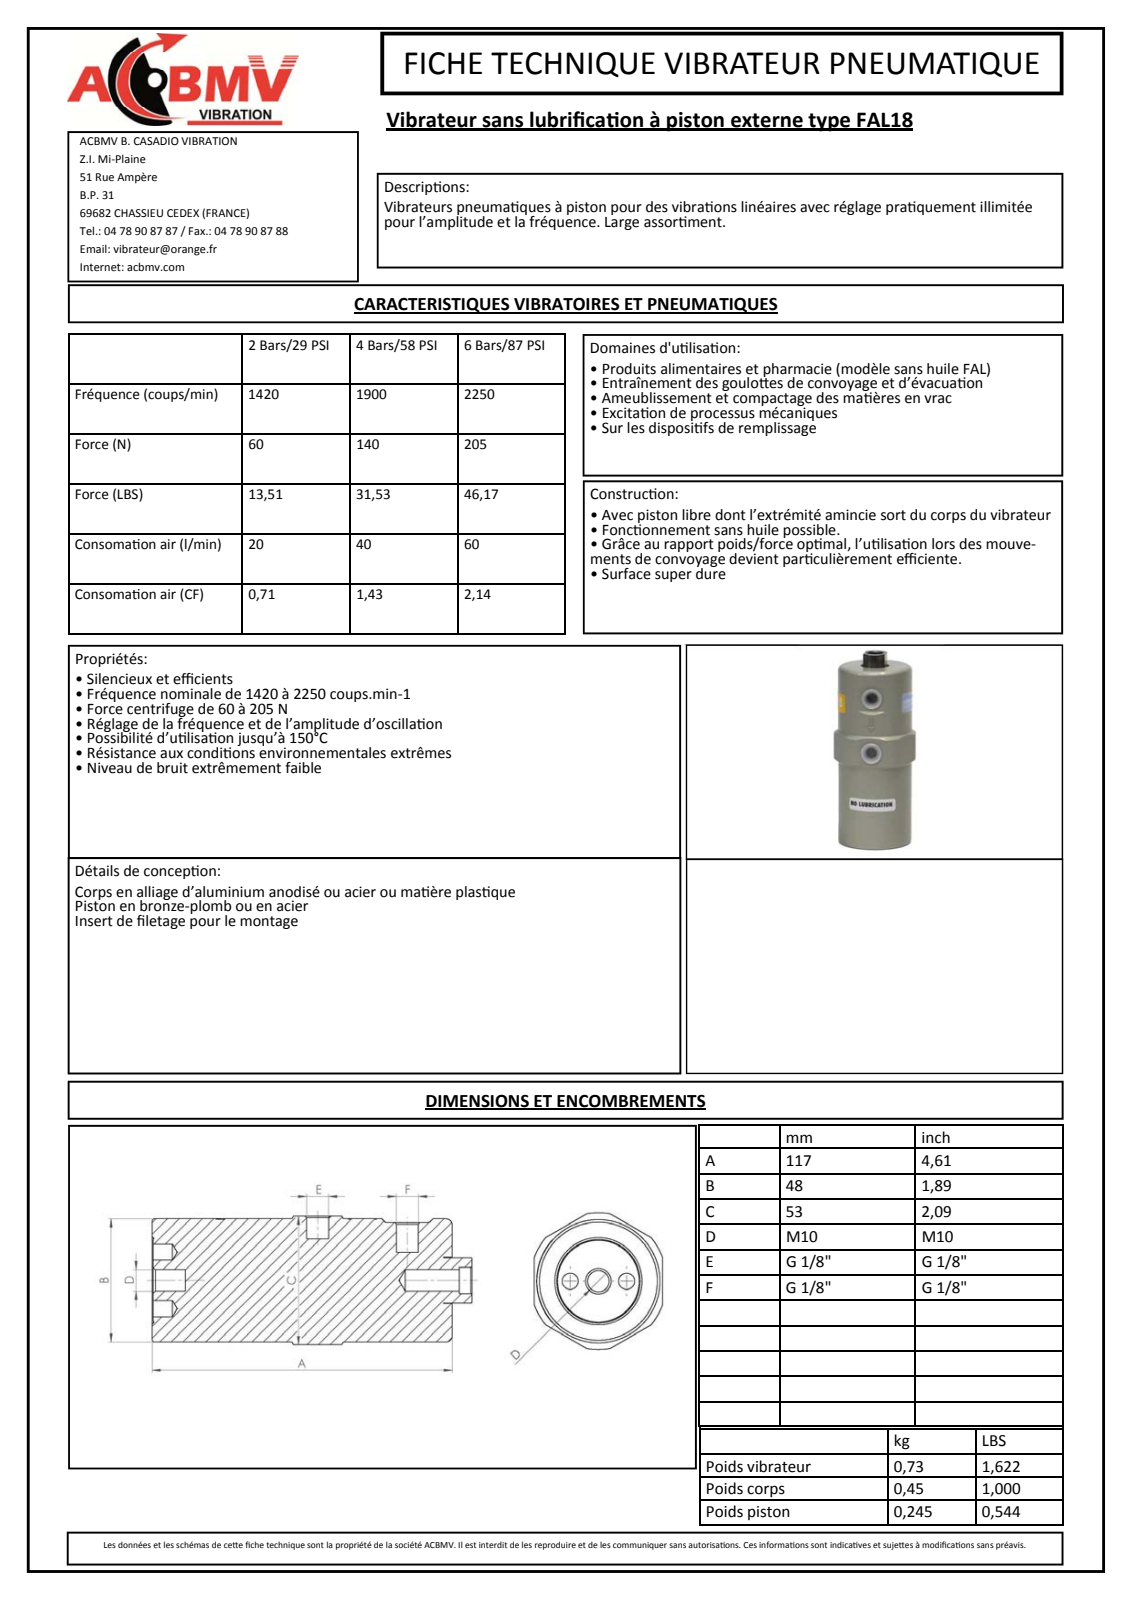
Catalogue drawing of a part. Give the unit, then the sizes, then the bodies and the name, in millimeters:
Units: millimetres
Overall size (bounding box): 124.7 × 53.3 × 50
Round holes (diameter × count): ⌀6.3 ×2, ⌀8.57 ×2, ⌀8.38 ×1, ⌀10.3 ×1, ⌀18 ×1
Round bosses / shafts (diameter × count): ⌀48 ×1, ⌀17.7 ×1
Partial cylindrical surfaces — rounded edges, fillets, slot ends (radius × count): R1.5 ×8, R11 ×1, R16.19 ×1, R23.8 ×1, R24.08 ×1, R24.1 ×1, R26.65 ×1
Main face-to-face distances: 50, 117, 116.6, 0.4, 47.5, 2.5, 7.7, 124.3, 124.7, 14
Hole centre spacings: 11, 22, 35
Volume: 214 042 mm³ · Surface area: 24 429 mm²
Bodies: 1 solid, 437 faces (177 planar, 72 cylindrical, 188 other)
Part name (STEP PRODUCT): 9718-00-M
STEP written by: Autodesk Inventor 2011 (CONFIG_CONTROL_DESIGN)
